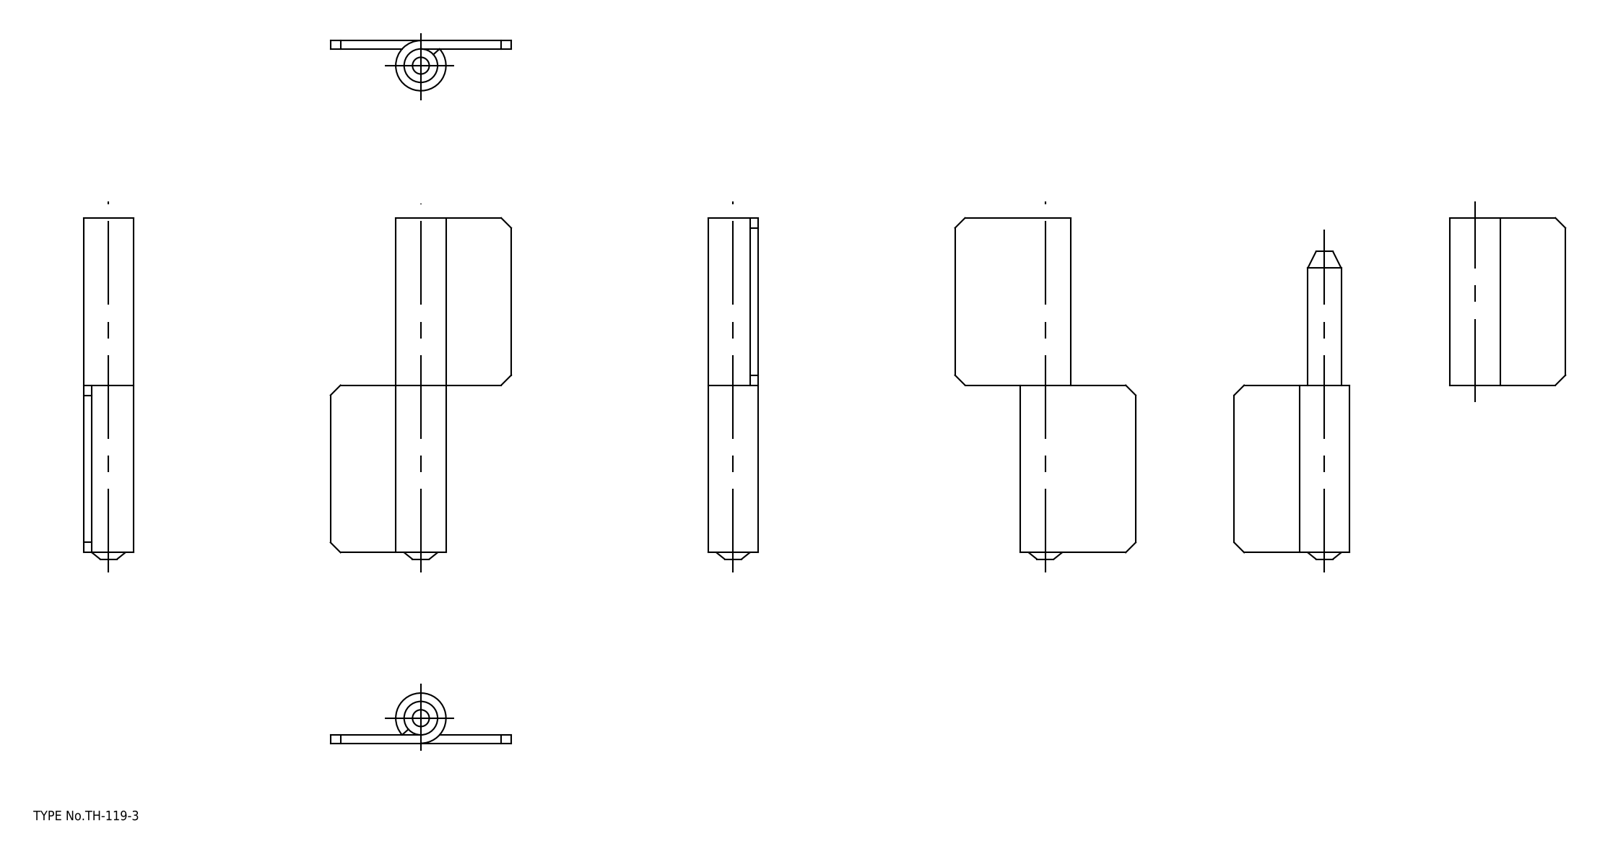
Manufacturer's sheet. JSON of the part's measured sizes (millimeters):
{"part_name": "ヒンジピース(A)組立; ヒンジピース(B)", "step_written_by": "spGate 16.7.1 (AUTOMOTIVE_DESIGN)", "units": "millimeters", "bodies": {"solids": 2, "faces": 27, "planar": 18, "cylindrical": 5, "other": 4}, "overall_size": [102, 54, 15], "volume_mm3": 22211, "surface_area_mm2": 13455, "round_bosses_or_shafts": [[15, 1], [10, 1]], "face_to_face_distances": [2.5, 50, 100, 54, 10, 102, 40, 90, 92, 52]}
